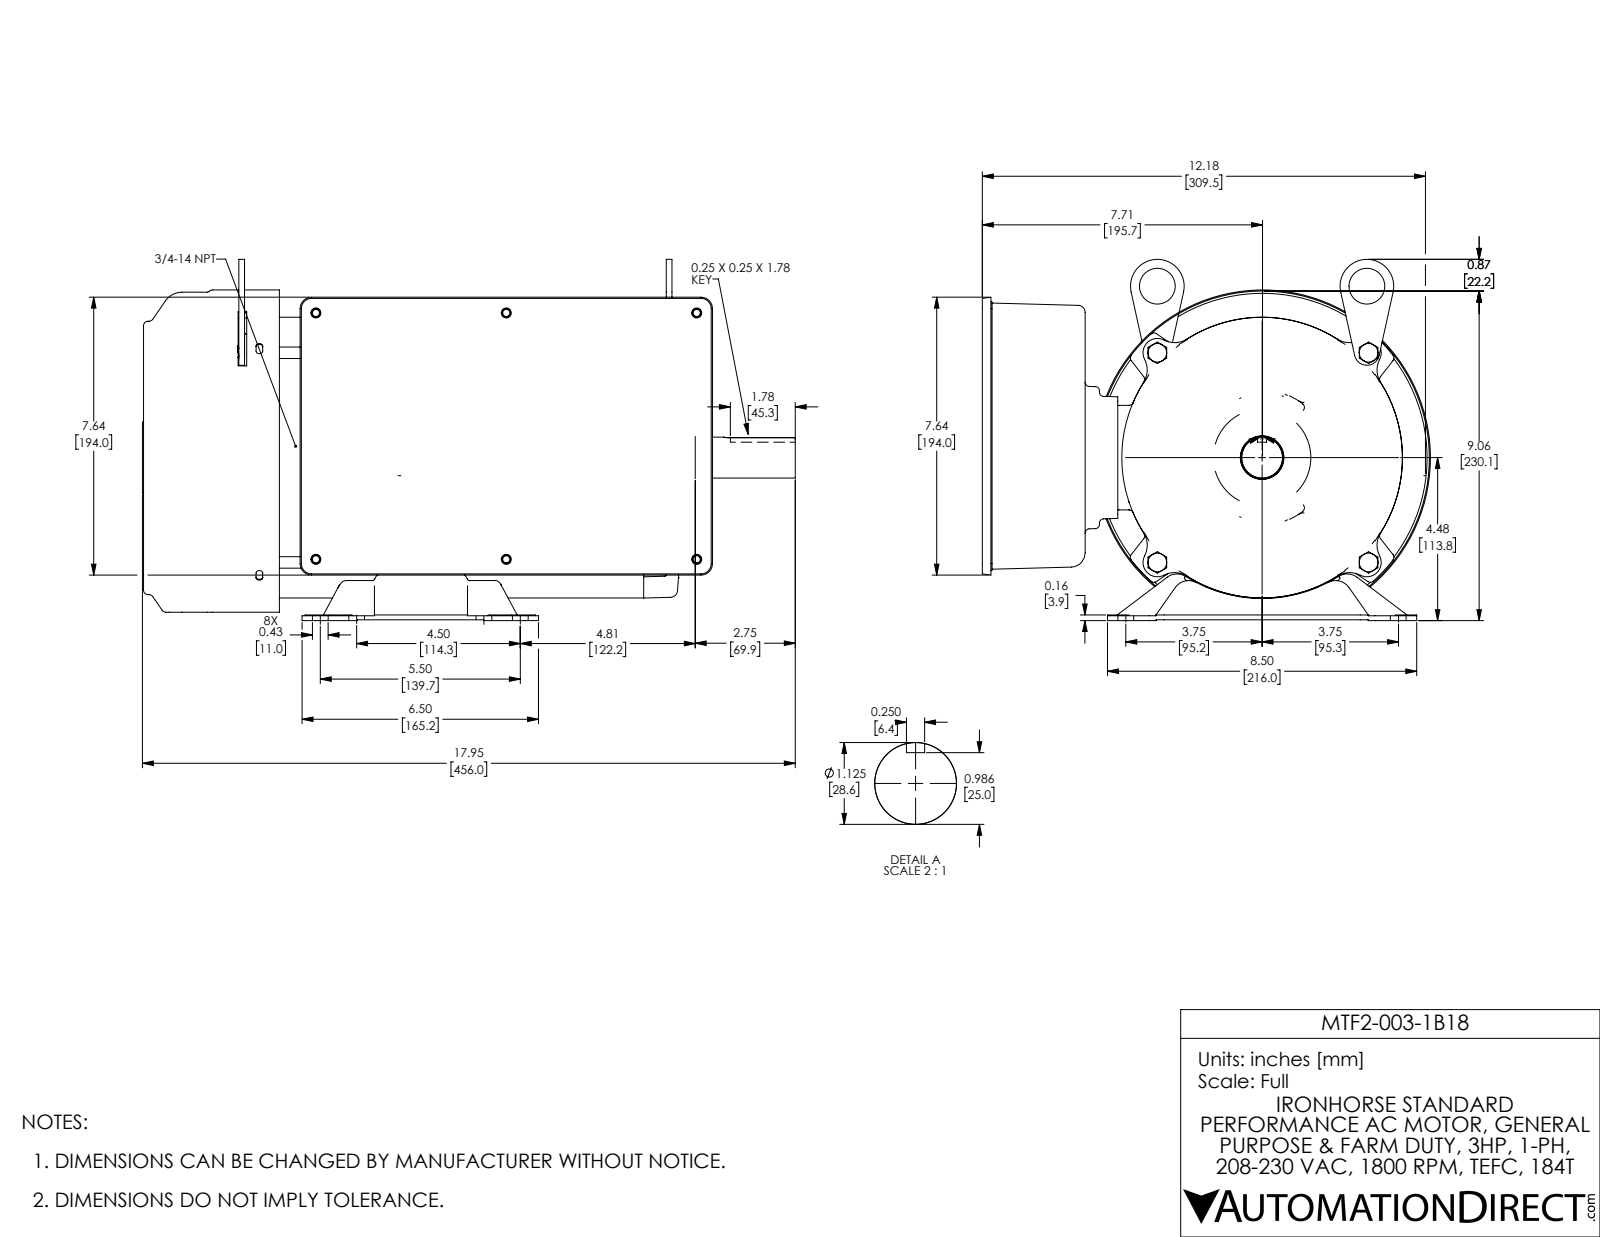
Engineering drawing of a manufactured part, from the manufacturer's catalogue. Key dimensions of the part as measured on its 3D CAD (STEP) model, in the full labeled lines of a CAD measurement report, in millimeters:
Part name (STEP PRODUCT): MTF2-003-1B18
STEP written by: SolidWorks 2017 (AUTOMOTIVE_DESIGN)
Units: millimetres
Bodies: 23 solids, 3305 faces (1074 planar, 905 cylindrical, 1326 other)
Overall size (bounding box): 456 × 313 × 252.2
Volume: 2 607 000 mm³ · Surface area: 1 283 000 mm²
Round holes (diameter × count): ⌀5 ×12, ⌀7 ×8, ⌀11 ×8, ⌀6 ×6, ⌀9.4 ×5, ⌀4.2 ×4, ⌀7.1 ×4, ⌀9.3 ×4, ⌀25 ×2, ⌀19 ×1, ⌀19.6 ×1, ⌀24 ×1
Round bosses / shafts (diameter × count): ⌀11.3 ×4, ⌀8 ×4, ⌀6.7 ×4, ⌀234.6 ×1, ⌀231.4 ×1, ⌀196 ×1, ⌀190.9 ×1, ⌀40 ×1
Partial cylindrical surfaces — rounded edges, fillets, slot ends (radius × count): R1.5 ×53, R5 ×51, R1 ×45, R3 ×42, R2 ×18, R4 ×17, R0.5 ×10, R3.2 ×9
Main face-to-face distances: 1, 4, 71.8, 66.8, 67.8, 70.8, 0.8, 5, 56, 56.8
Hole centre spacings: 147.5, 147, 0.6, 25.4, 50, 69.1, 69.5, 97.7
